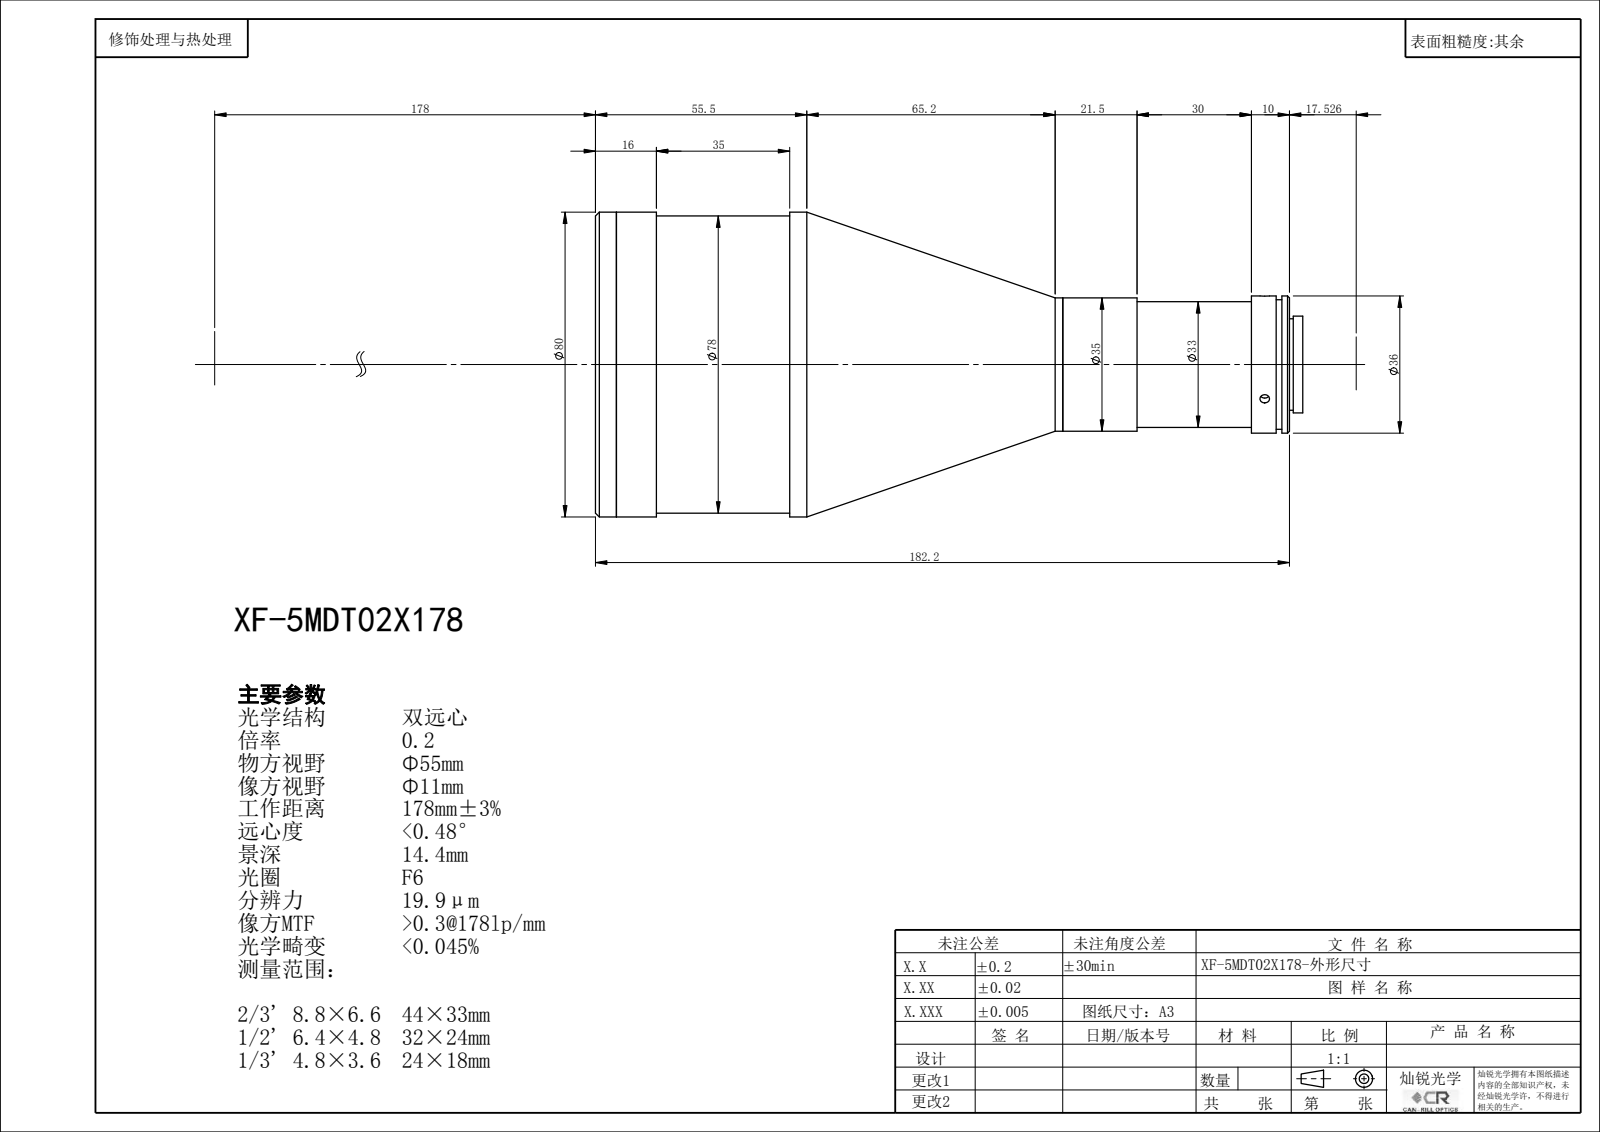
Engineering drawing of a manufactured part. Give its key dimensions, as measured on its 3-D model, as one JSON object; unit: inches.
{"part_name": "XF-5MDT02X178", "step_written_by": "SolidWorks 2014 (CONFIG_CONTROL_DESIGN)", "units": "inches", "bodies": {"solids": 0, "faces": 84, "planar": 26, "cylindrical": 46, "other": 12}, "overall_size": [7.313, 3.15, 3.15], "round_holes": [[0.098, 3], [0.787, 1], [0.843, 1], [2.756, 1], [2.874, 1], [2.992, 1]], "round_bosses_or_shafts": [[3.15, 1], [3.071, 1], [1.417, 1], [1.378, 1], [1.339, 1], [1.299, 1], [1.102, 1], [1, 1]], "face_to_face_distances": [7.096, 0.079, 7.175, 0.138, 0.217, 7.052, 6.974, 0.122, 6.958, 6.88]}
